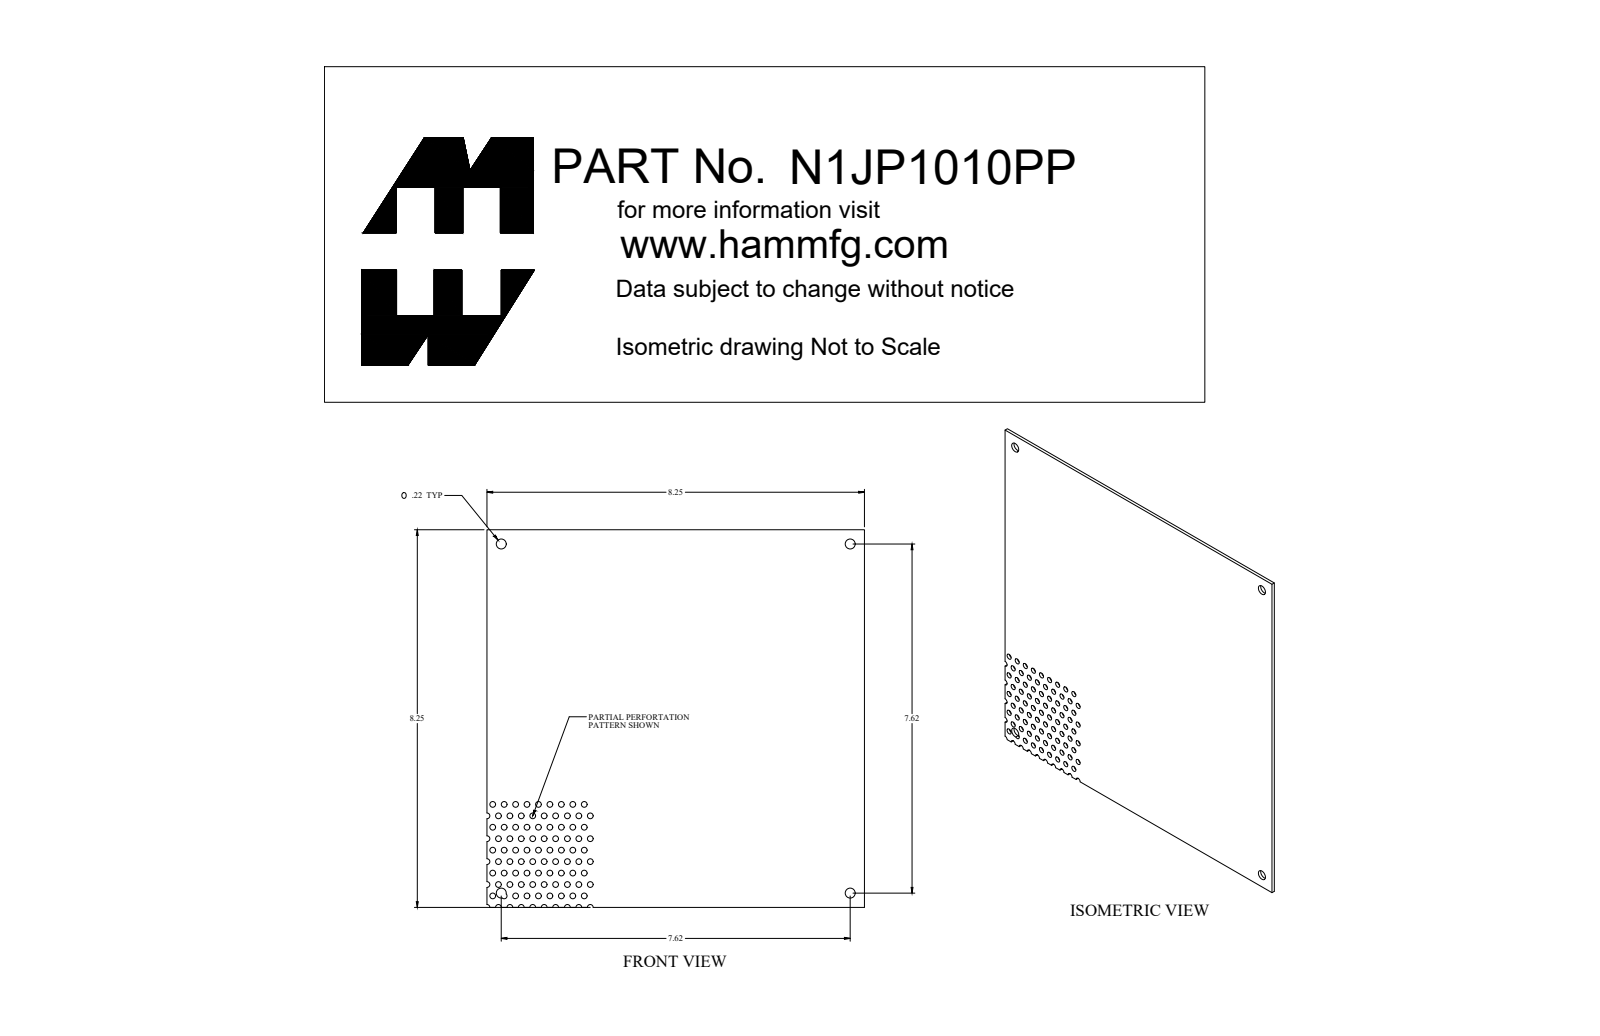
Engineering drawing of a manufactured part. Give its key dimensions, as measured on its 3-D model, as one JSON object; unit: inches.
{"part_name": "N1JP1010PP", "step_written_by": "SolidWorks 2018 (AUTOMOTIVE_DESIGN)", "units": "inches", "bodies": {"solids": 1, "faces": 203, "planar": 19, "cylindrical": 184, "other": 0}, "overall_size": [8.25, 8.25, 0.072], "volume_in3": 4.813, "surface_area_in2": 138.6, "round_holes": [[0.125, 58], [0.125, 22], [0.218, 4]], "partial_cylinders_radius": [[0.063, 12], [0.062, 3]], "face_to_face_distances": [0.072, 8.25], "hole_center_spacings": [0.5, 0.25, 0.559, 0.707, 0.75, 0.28, 0.902, 0.279]}
